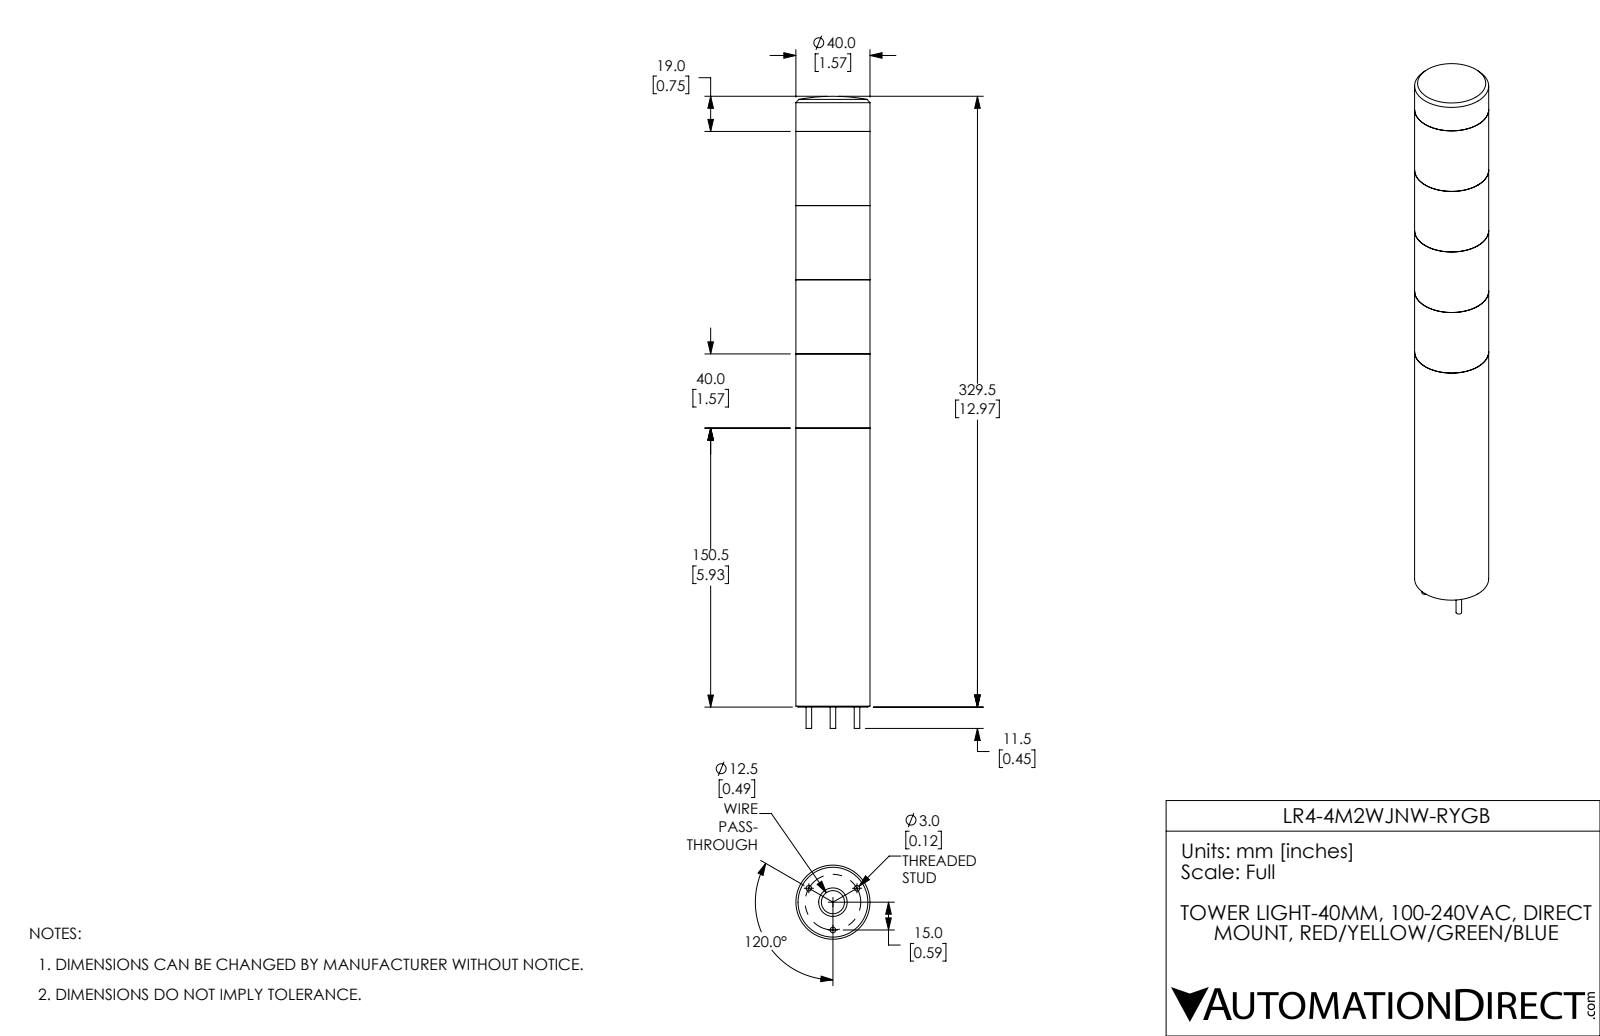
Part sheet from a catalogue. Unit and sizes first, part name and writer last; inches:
Units: inches
Overall size (bounding box): 13.424 × 1.575 × 1.575
Round holes (diameter × count): ⌀0.492 ×1, ⌀0.606 ×1, ⌀1.366 ×1, ⌀1.386 ×1, ⌀1.461 ×1, ⌀1.463 ×1
Round bosses / shafts (diameter × count): ⌀0.118 ×3, ⌀1.575 ×1, ⌀1.484 ×1
Main face-to-face distances: 1.575, 3.15, 4.724, 6.299, 0.406, 1.98, 1.169, 0.126, 0.28, 3.555
Volume: 25.15 in³ · Surface area: 105.8 in²
Bodies: 6 solids, 104 faces (37 planar, 64 cylindrical, 3 other)
Part name (STEP PRODUCT): LR4-4M2WJNW-RYGB
STEP written by: SolidWorks 2017 (AUTOMOTIVE_DESIGN)
